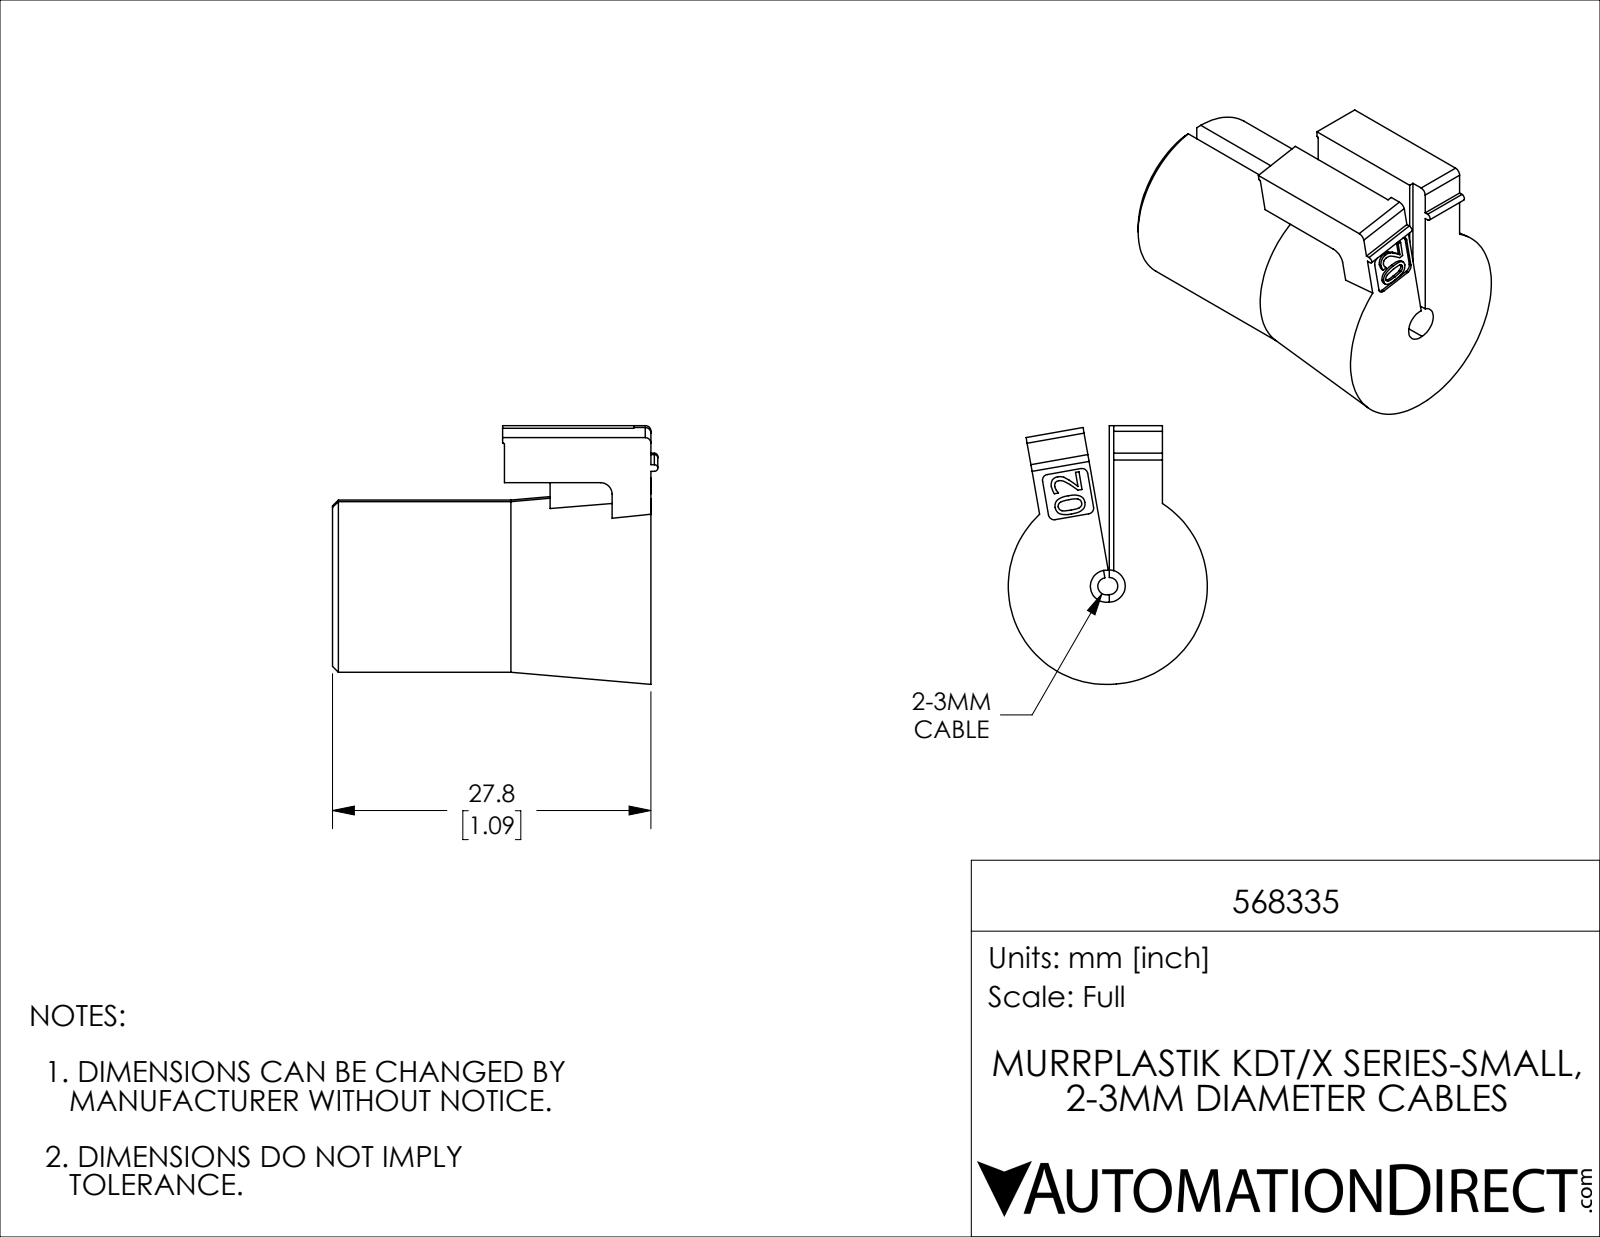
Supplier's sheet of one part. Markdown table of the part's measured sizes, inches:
| quantity | value |
| --- | --- |
| part name | 568335 |
| STEP written by | SolidWorks 2019 (CONFIG_CONTROL_DESIGN) |
| units | inches |
| bodies | 1 solid, 119 faces (58 planar, 25 cylindrical, 36 other) |
| overall size | 1.118 × 0.889 × 0.684 |
| volume | 0.34 in³ |
| surface area | 4.393 in² |
| partial cylindrical surfaces (radius × count) | 0.02 × 6, 0.004 × 2, 0.012 × 2, 0.03 × 2, 0.039 × 2, 0.055 × 2, 0.295 × 2 |
| main face-to-face distances | 1.094, 0.183, 0.157, 0.016, 0.504, 0.591, 0.167, 0.199, 0.346, 0.748 |
